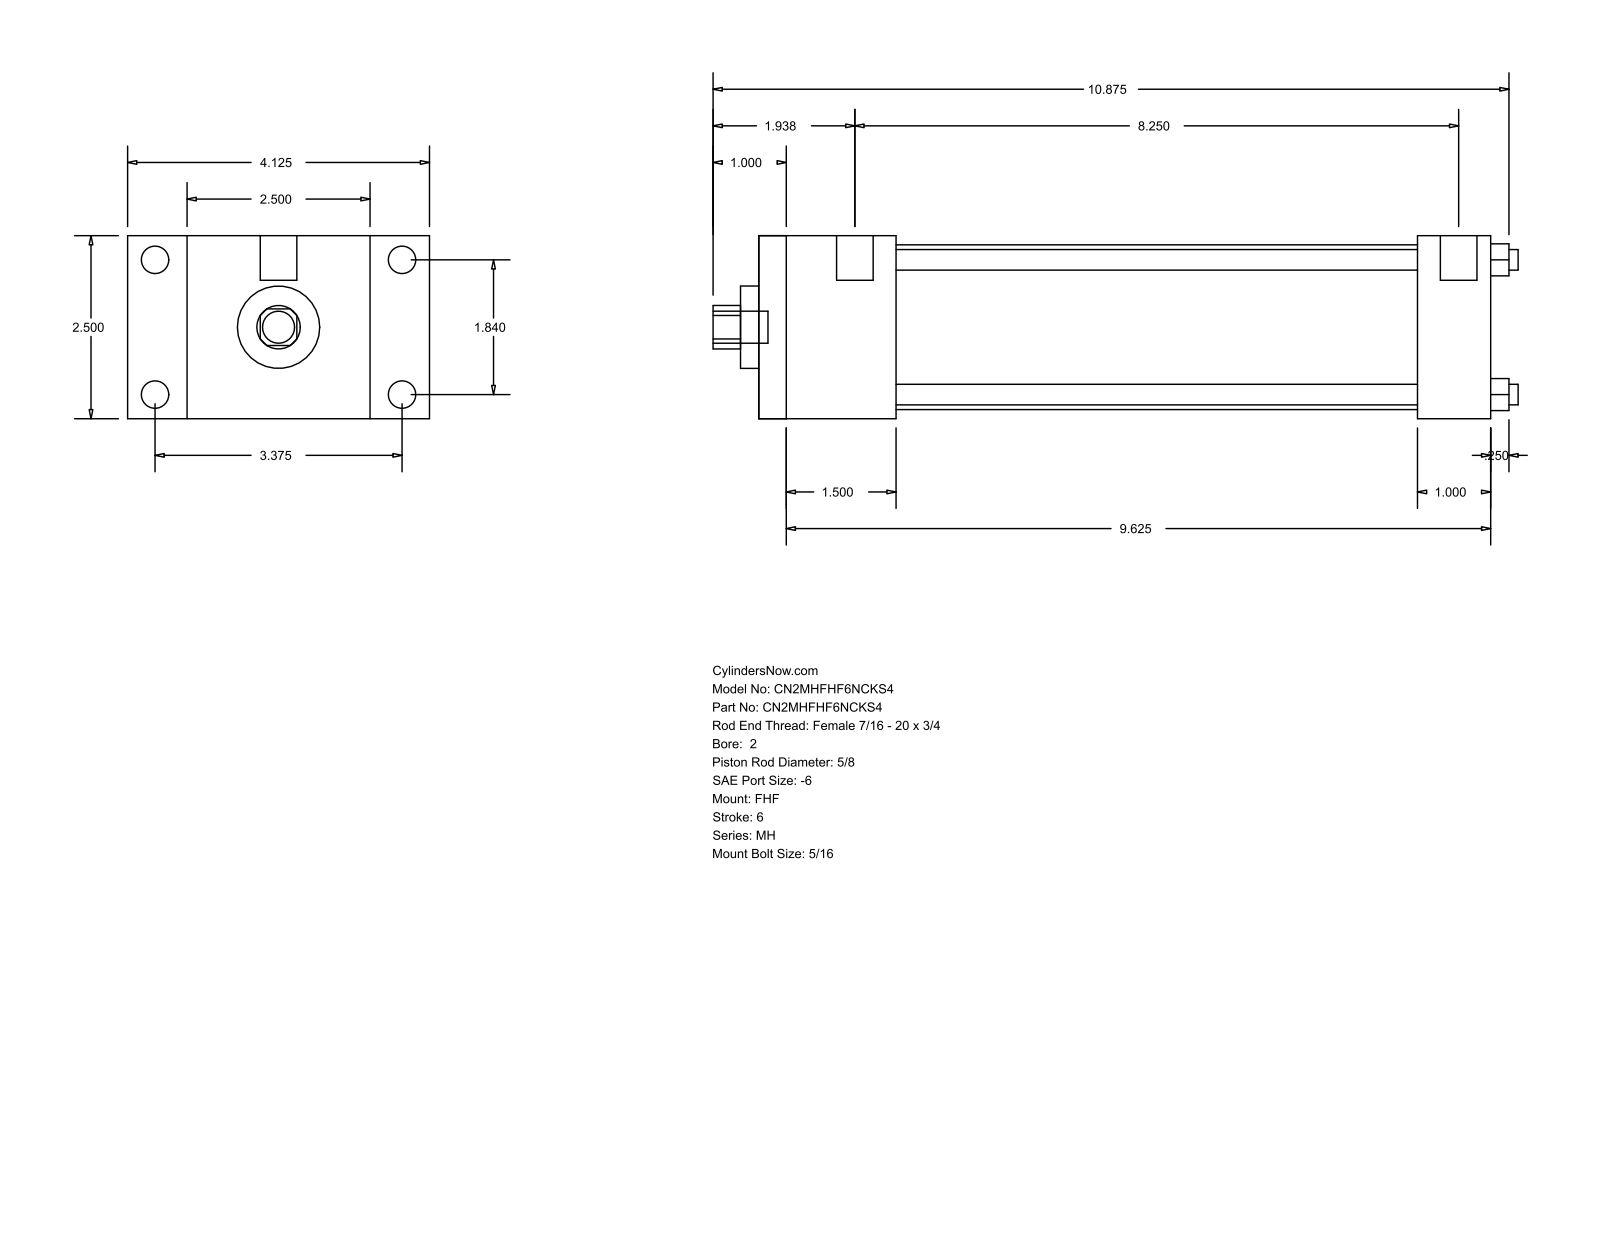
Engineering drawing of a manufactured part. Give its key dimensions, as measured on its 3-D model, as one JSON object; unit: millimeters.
{"part_name": "MH_FHF__0200_0.625", "step_written_by": "GSSL Pune (CONFIG_CONTROL_DESIGN)", "units": "millimeters", "bodies": {"solids": 0, "faces": 88, "planar": 60, "cylindrical": 28, "other": 0}, "overall_size": [279.4, 104.78, 63.5], "round_holes": [[7.14, 4], [15.88, 1], [28.57, 1], [57.15, 1]], "round_bosses_or_shafts": [[9.53, 4], [5.56, 4], [12.7, 2], [11.11, 1]], "partial_cylinders_radius": [[7.54, 1]], "face_to_face_distances": [63.5, 47.62, 254, 206.38, 20.64, 84.14, 104.78, 228.59, 180.97, 25.41], "hole_center_spacings": [33.05, 46.74, 66.1]}
